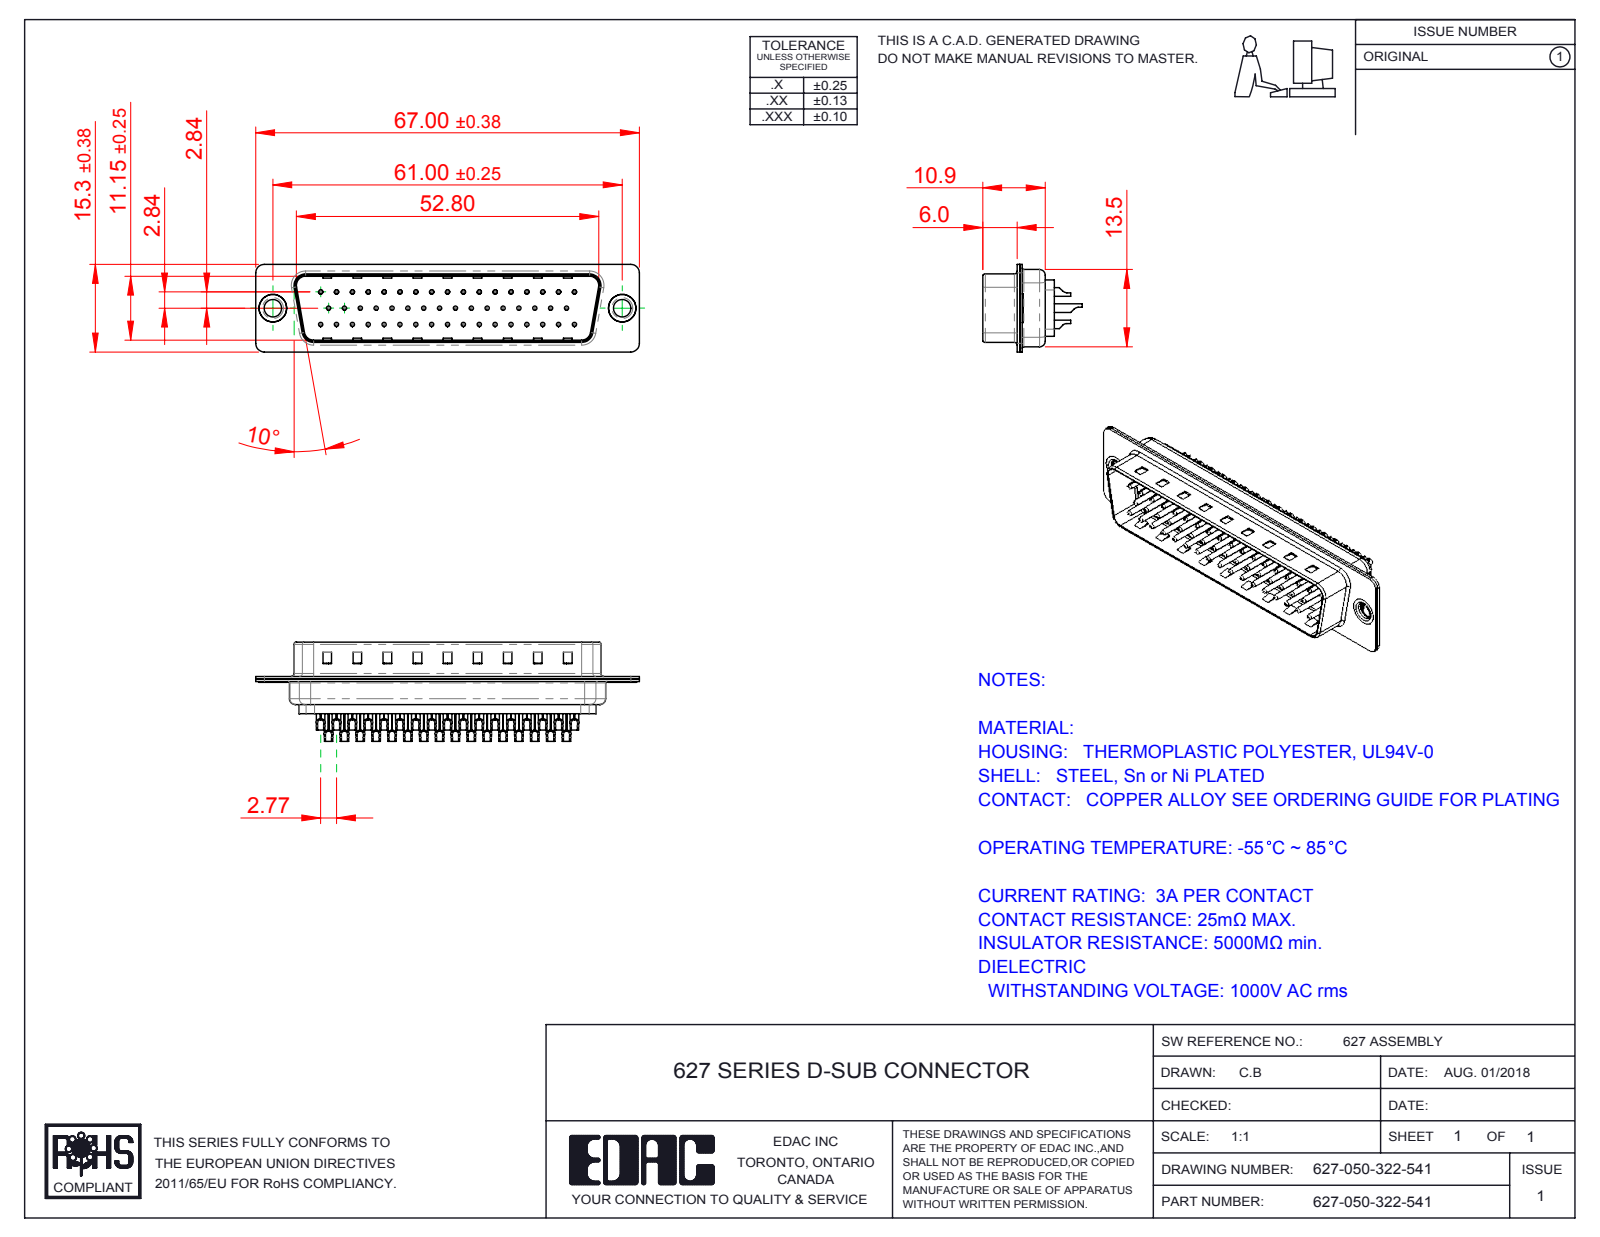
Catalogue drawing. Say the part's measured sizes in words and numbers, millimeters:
The part is named "627 Housing_50 LP; 627-050-322-541; 627 Thru Hole Rivet; 627 Contact Row 3_22L (+4 more)". Its 3-D file was written by "SolidWorks 2016 (CONFIG_CONTROL_DESIGN)". It is 55 solids with 3586 faces: 903 planar, 1575 cylindrical and 1108 other. Overall it measures 67 by 17.35 by 15.3 millimeters. Its volume is 4 389 cubic millimeters and its surface area 12 813 square millimeters. Round holes: 50 of diameter 0.35, 50 of diameter 1.1, 50 of diameter 1.6, 2 of diameter 3.05, 2 of diameter 4, 2 of diameter 4.8. Round bosses or shafts: 50 of diameter 2, 50 of diameter 1.5, 50 of diameter 0.75, 2 of diameter 5, 2 of diameter 4.9, 2 of diameter 3.55. Partial cylindrical surfaces (rounded edges, fillets, slot ends): 16 of radius 1.5, 12 of radius 2, 8 of radius 0.5, 8 of radius 1.6, 7 of radius 1, 4 of radius 0.25, 4 of radius 0.6, 4 of radius 0.65. The main face-to-face distances are 0.4, 0.45, 11.55, 0.9, 6.05, 6.5, 0.78, 12.33, 1.95, 0.77. The hole center spacings are 3.16, 2.77, 5.54, 8.31, 11.08, 13.85, 16.62, 5.03.
